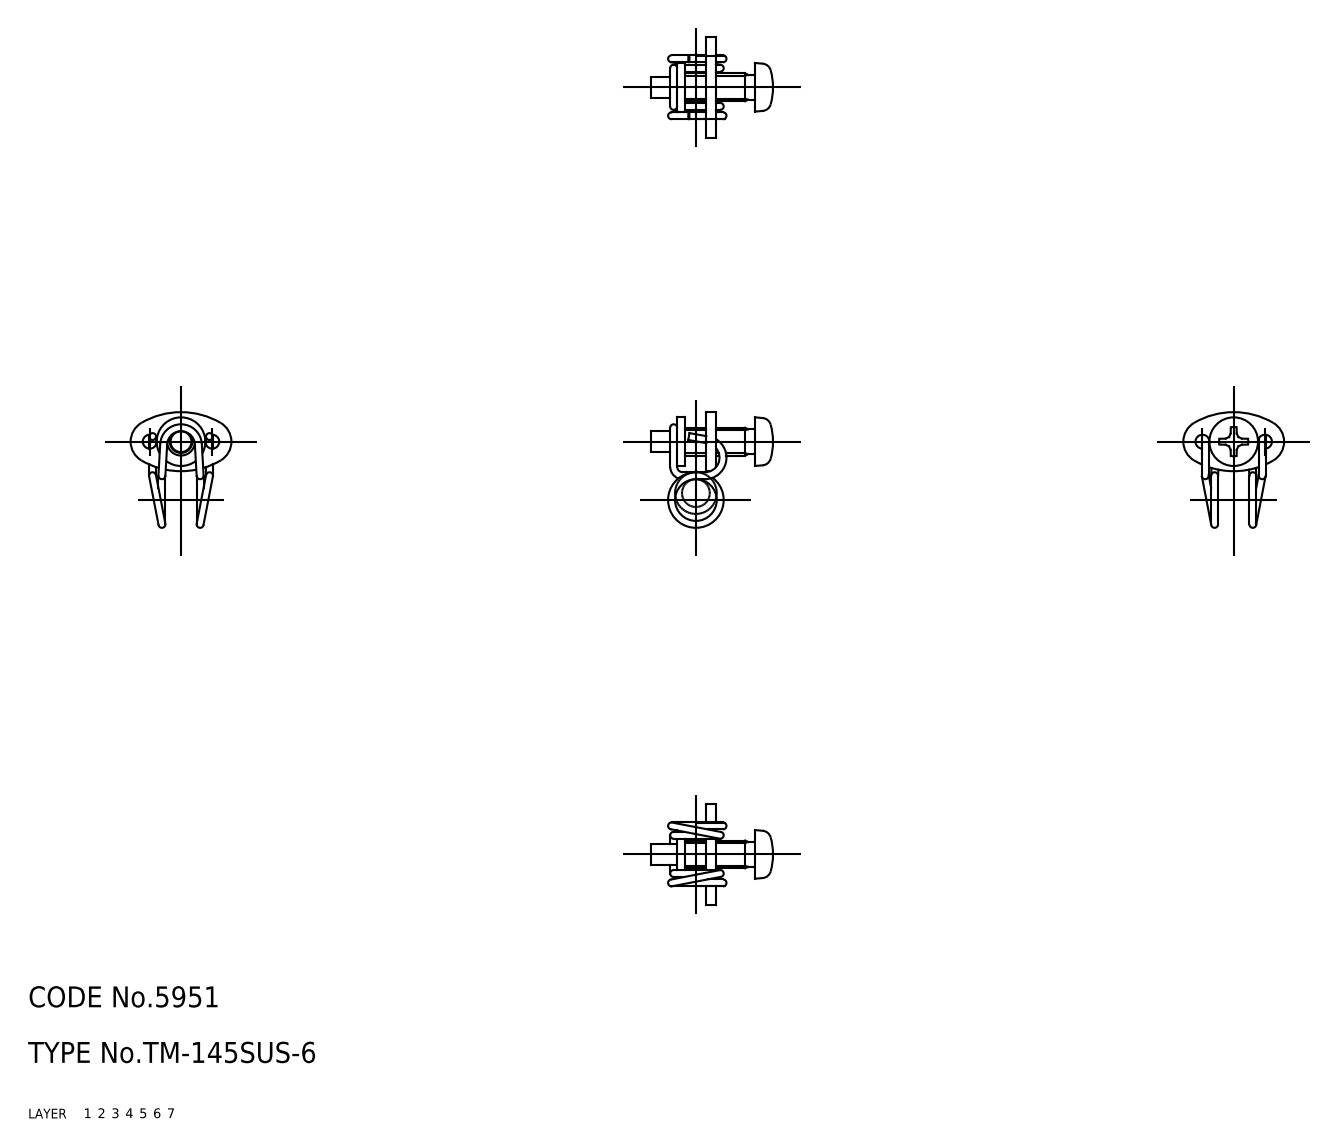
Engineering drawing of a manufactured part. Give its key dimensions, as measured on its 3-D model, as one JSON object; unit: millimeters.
{"part_name": "67120835; 67120848; 67120861", "step_written_by": "CADfix (AUTOMOTIVE_DESIGN)", "units": "millimeters", "bodies": {"solids": 3, "faces": 85, "planar": 0, "cylindrical": 0, "other": 85}, "overall_size": [17.55, 16.65, 14.5], "volume_mm3": 454, "surface_area_mm2": 895}
